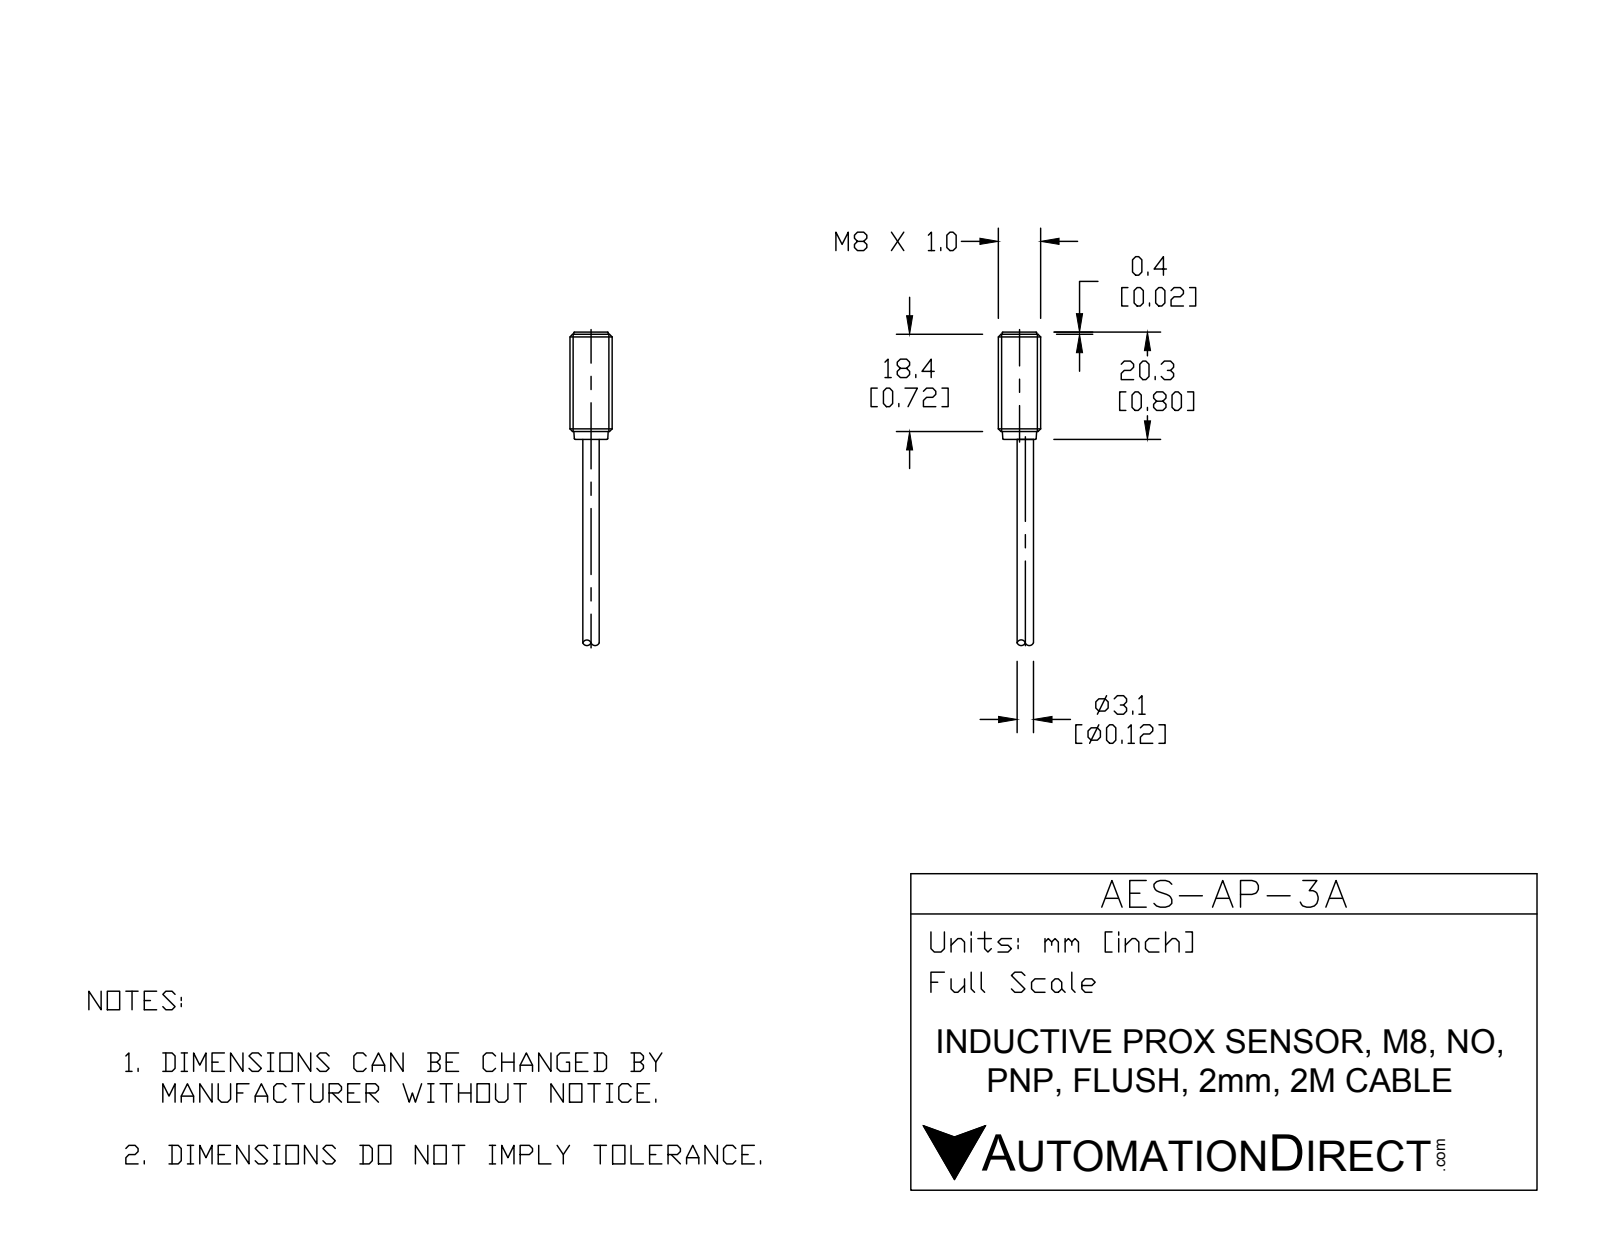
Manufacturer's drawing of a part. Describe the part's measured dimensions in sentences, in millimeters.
The part is named "AES-AP-3A". Its 3-D file was written by "SolidWorks 2015 (CONFIG_CONTROL_DESIGN)". It is 1 solid with 21 faces: 5 planar, 6 cylindrical and 10 other. Overall it measures 69.9 by 8 by 8 millimeters. Its volume is 1 335 cubic millimeters and its surface area 1 054 square millimeters. Round bosses or shafts: 1 of diameter 8, 1 of diameter 6.5, 1 of diameter 3.1. The main face-to-face distances are 19.9, 50, 69.9, 69.5, 19.5, 0.4, 51.5, 1.5, 18, 18.4.
